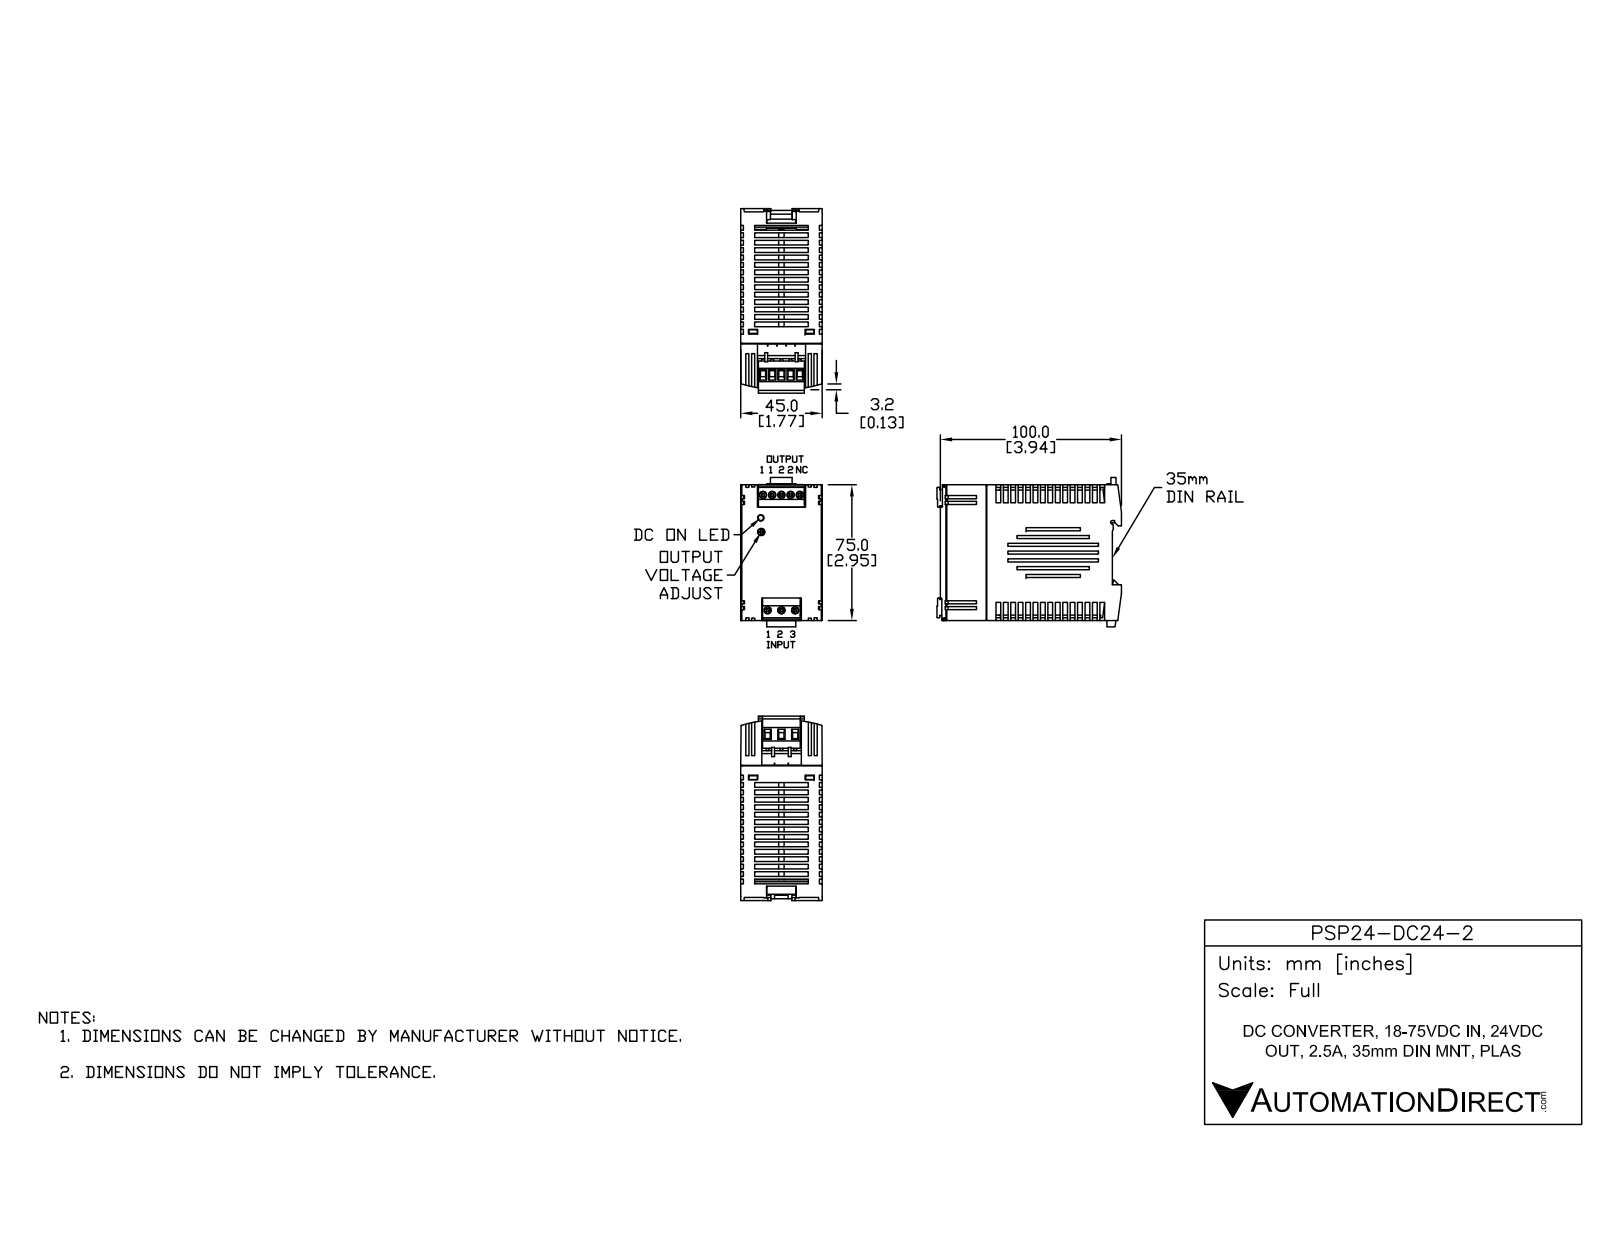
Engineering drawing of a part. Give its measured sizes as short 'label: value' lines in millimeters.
name: PSP24-DC24-2
written by: SolidWorks 2015 (AUTOMOTIVE_DESIGN)
unit: mm
bodies: 0 solids, 1218 faces (1068 planar, 145 cylindrical, 5 other)
size: 101.86 × 82.49 × 45.03
holes: 8× ⌀4, 1× ⌀3.44, 1× ⌀3.86, 1× ⌀3.91
bosses: 2× ⌀1.4, 1× ⌀0.51
rounds: 30× R0.25, 5× R0.2, 2× R1, 1× R0.3, 1× R0.75, 1× R1.5, 1× R3.5, 1× R5.5
face distances: 1.5, 43.49, 44.99, 73.5, 41.99, 72, 3, 75, 3.5, 6.5
hole spacings: 5.08, 63.73, 10.16, 15.24, 7.62, 7.84, 63.88, 64.13
